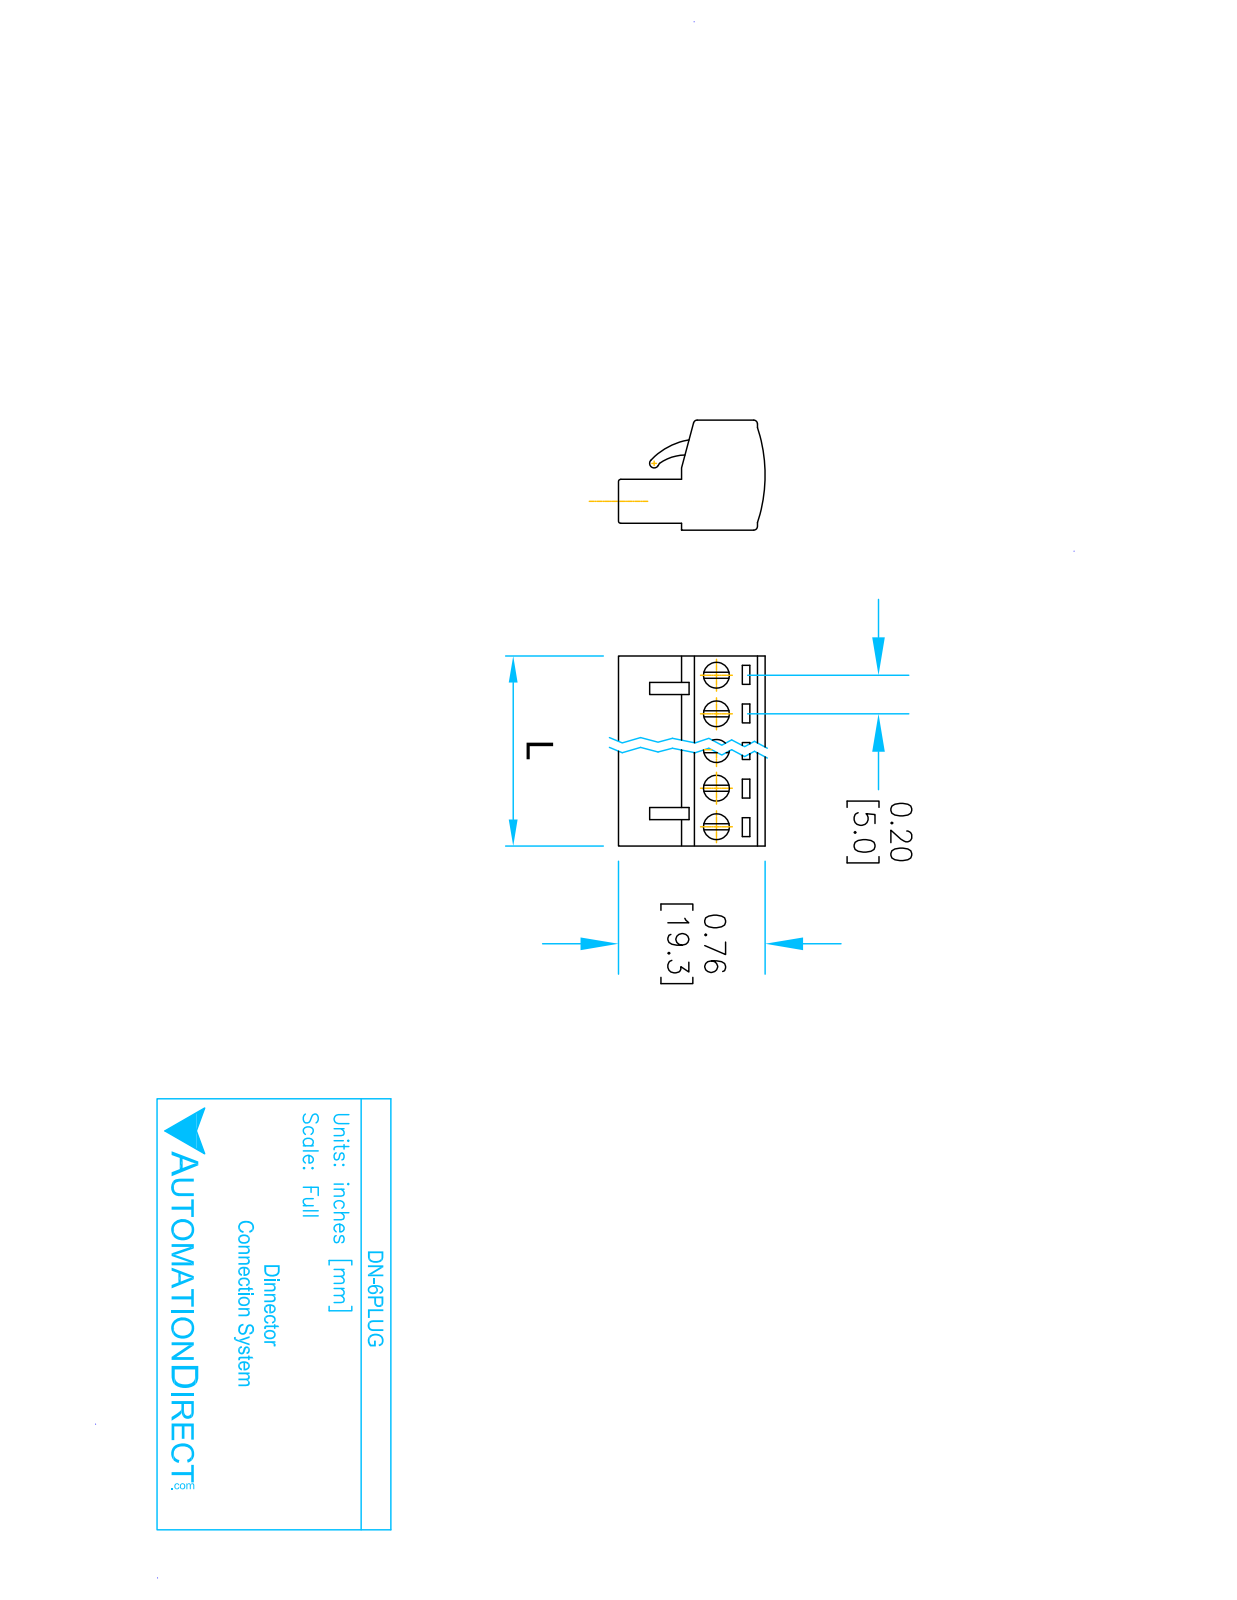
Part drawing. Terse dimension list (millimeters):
name: 49006_S; 49001_S; 49001_S_49002_SENZA DENTE; 49002_S
written by: SolidWorks 2013 (AUTOMOTIVE_DESIGN)
unit: mm
bodies: 5 solids, 542 faces (379 planar, 133 cylindrical, 30 other)
size: 30.48 × 19.3 × 14.5
volume: 5 218 mm³; area: 5 275 mm²
holes: 6× ⌀1.6, 6× ⌀2.5, 6× ⌀3.4, 6× ⌀3.6
bosses: 6× ⌀3
rounds: 6× R2.9, 3× R0.5, 2× R0.3, 1× R0.6, 1× R6, 1× R9, 1× R20.03
face distances: 5.08, 10.16, 15.24, 20.32, 6.7, 1, 25.4, 30.48, 14.5, 7.8
hole spacings: 5.08, 10.16, 15.24, 20.32, 25.4
